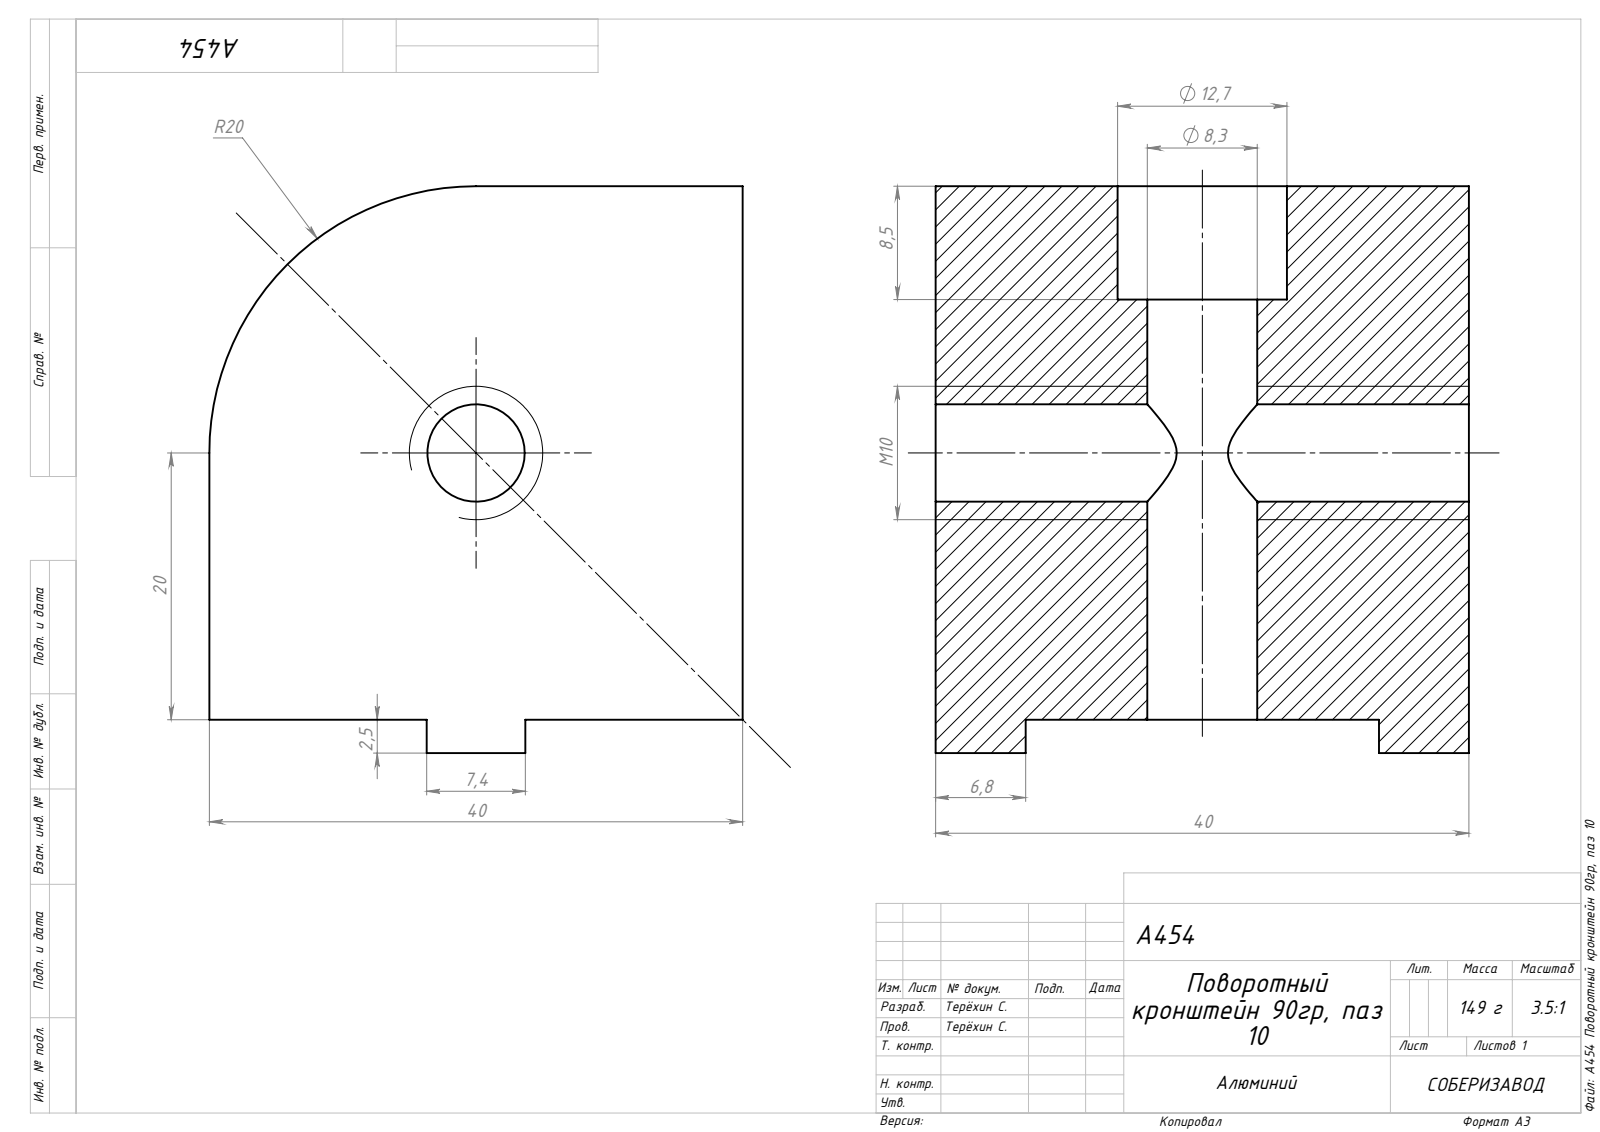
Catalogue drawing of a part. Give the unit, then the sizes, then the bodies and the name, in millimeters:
Units: millimetres
Overall size (bounding box): 42.5 × 40 × 40
Round holes (diameter × count): ⌀7.3 ×1, ⌀8.25 ×1, ⌀12.7 ×1
Partial cylindrical surfaces — rounded edges, fillets, slot ends (radius × count): R20 ×1
Main face-to-face distances: 40, 2.5, 42.5, 34, 31.5, 8.5, 16.3, 23.7, 6.75, 33.25
Volume: 56 704 mm³ · Surface area: 10 858 mm²
Bodies: 1 solid, 24 faces (15 planar, 9 cylindrical, 0 other)
Part name (STEP PRODUCT): A454 Поворотный кронштейн 90гр, паз 10
STEP written by: SolidWorks 2021 (AUTOMOTIVE_DESIGN)
